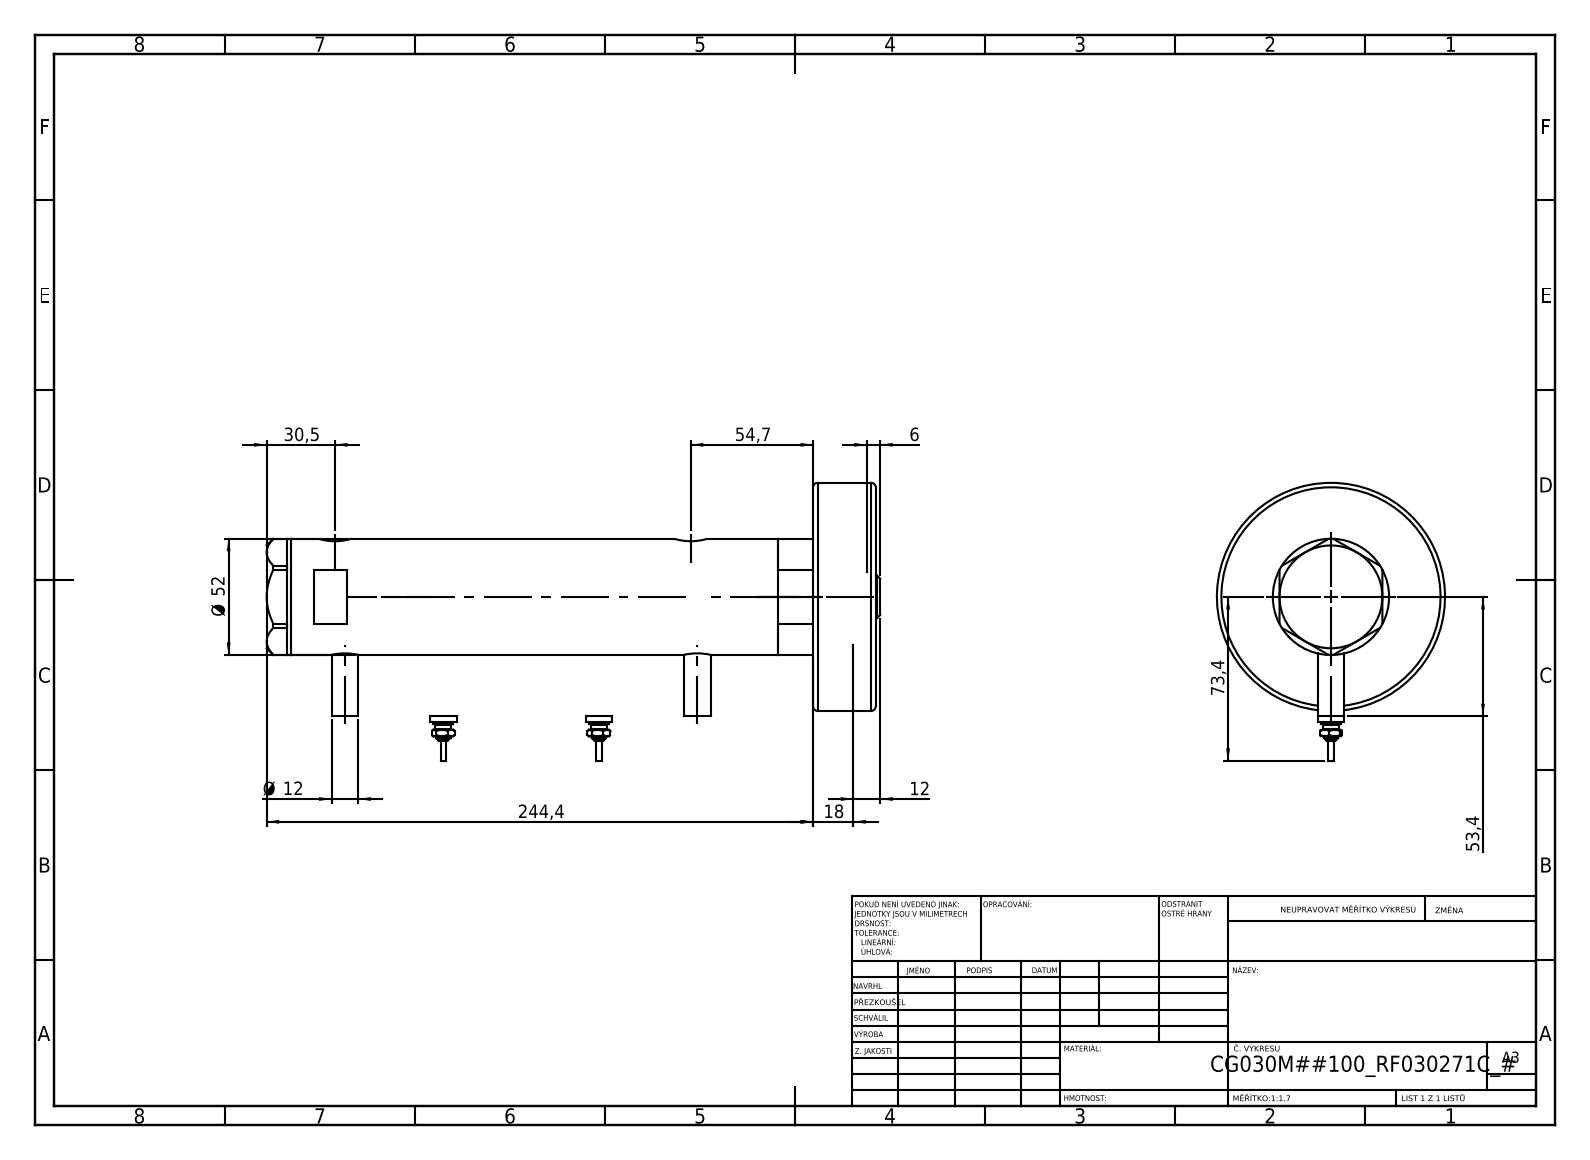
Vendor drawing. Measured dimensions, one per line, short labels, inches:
name: V270CG_FRONT; V270CG_271C; Switch; V270CG_MIDDLE (+2 more)
written by: SolidWorks 2019 (CONFIG_CONTROL_DESIGN)
unit: in
bodies: 7 solids, 236 faces (95 planar, 73 cylindrical, 68 other)
size: 10.803 × 4.898 × 4.016
volume: 42.57 in³; area: 209.5 in²
holes: 2× ⌀0.383, 2× ⌀0.492, 2× ⌀0.591, 1× ⌀0.256, 1× ⌀0.787, 1× ⌀0.846, 1× ⌀1.181, 1× ⌀1.299, 1× ⌀1.575, 1× ⌀1.732
bosses: 4× ⌀0.472, 2× ⌀0.354, 2× ⌀0.276, 2× ⌀0.177, 2× ⌀0.098, 1× ⌀4.016, 1× ⌀2.047, 1× ⌀1.496
face distances: 1.102, 9.189, 10.291, 7.146, 2.043, 3.146, 0.937, 6.209, 8.252, 9.354
hole spacings: 0.114, 0.177, 6.091, 6.205, 6.268, 6.382
